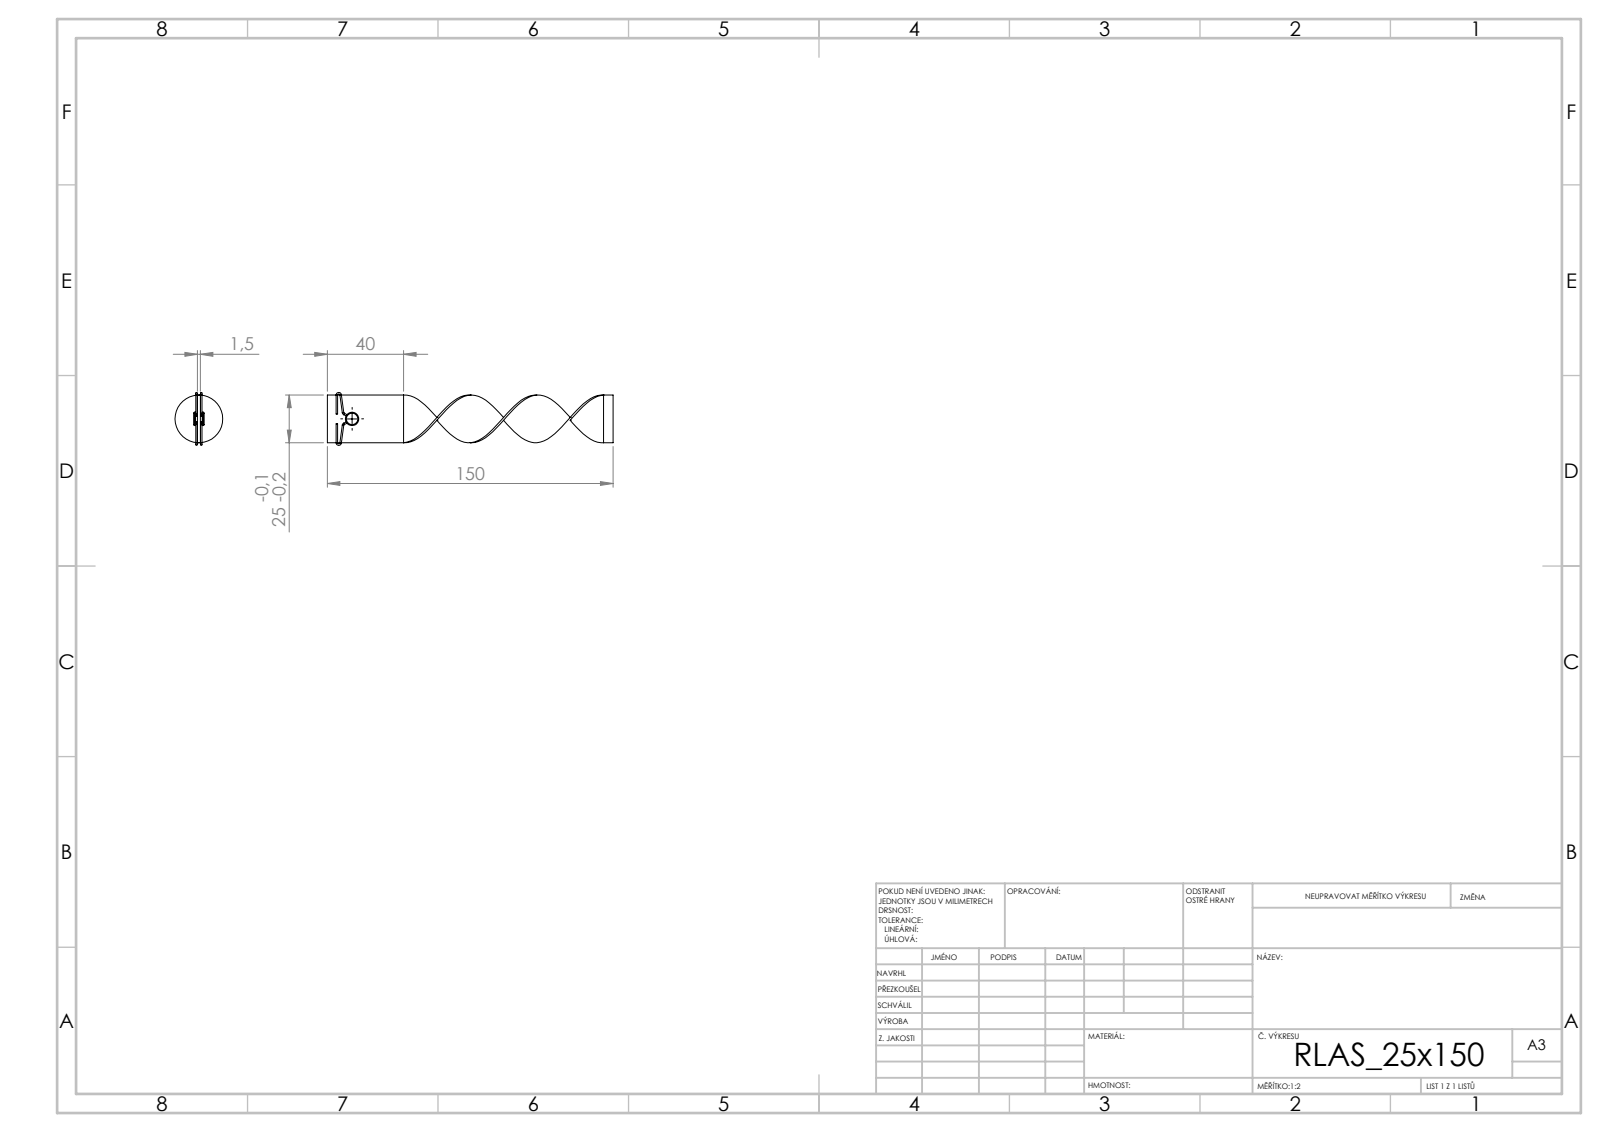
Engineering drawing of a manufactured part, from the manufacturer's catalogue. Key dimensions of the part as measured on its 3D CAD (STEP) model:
STEP written by: SolidWorks 2019 (CONFIG_CONTROL_DESIGN)
Units: millimetres
Bodies: 3 solids, 90 faces (18 planar, 40 cylindrical, 32 other)
Overall size (bounding box): 150 × 27.8 × 25.05
Volume: 5 790 mm³ · Surface area: 9 467 mm²
Round bosses / shafts (diameter × count): ⌀0.8 ×14, ⌀7 ×1, ⌀4 ×1
Main face-to-face distances: 1.5, 1, 3.5, 25, 2, 4.5, 2.5, 150, 5.5, 9.95
